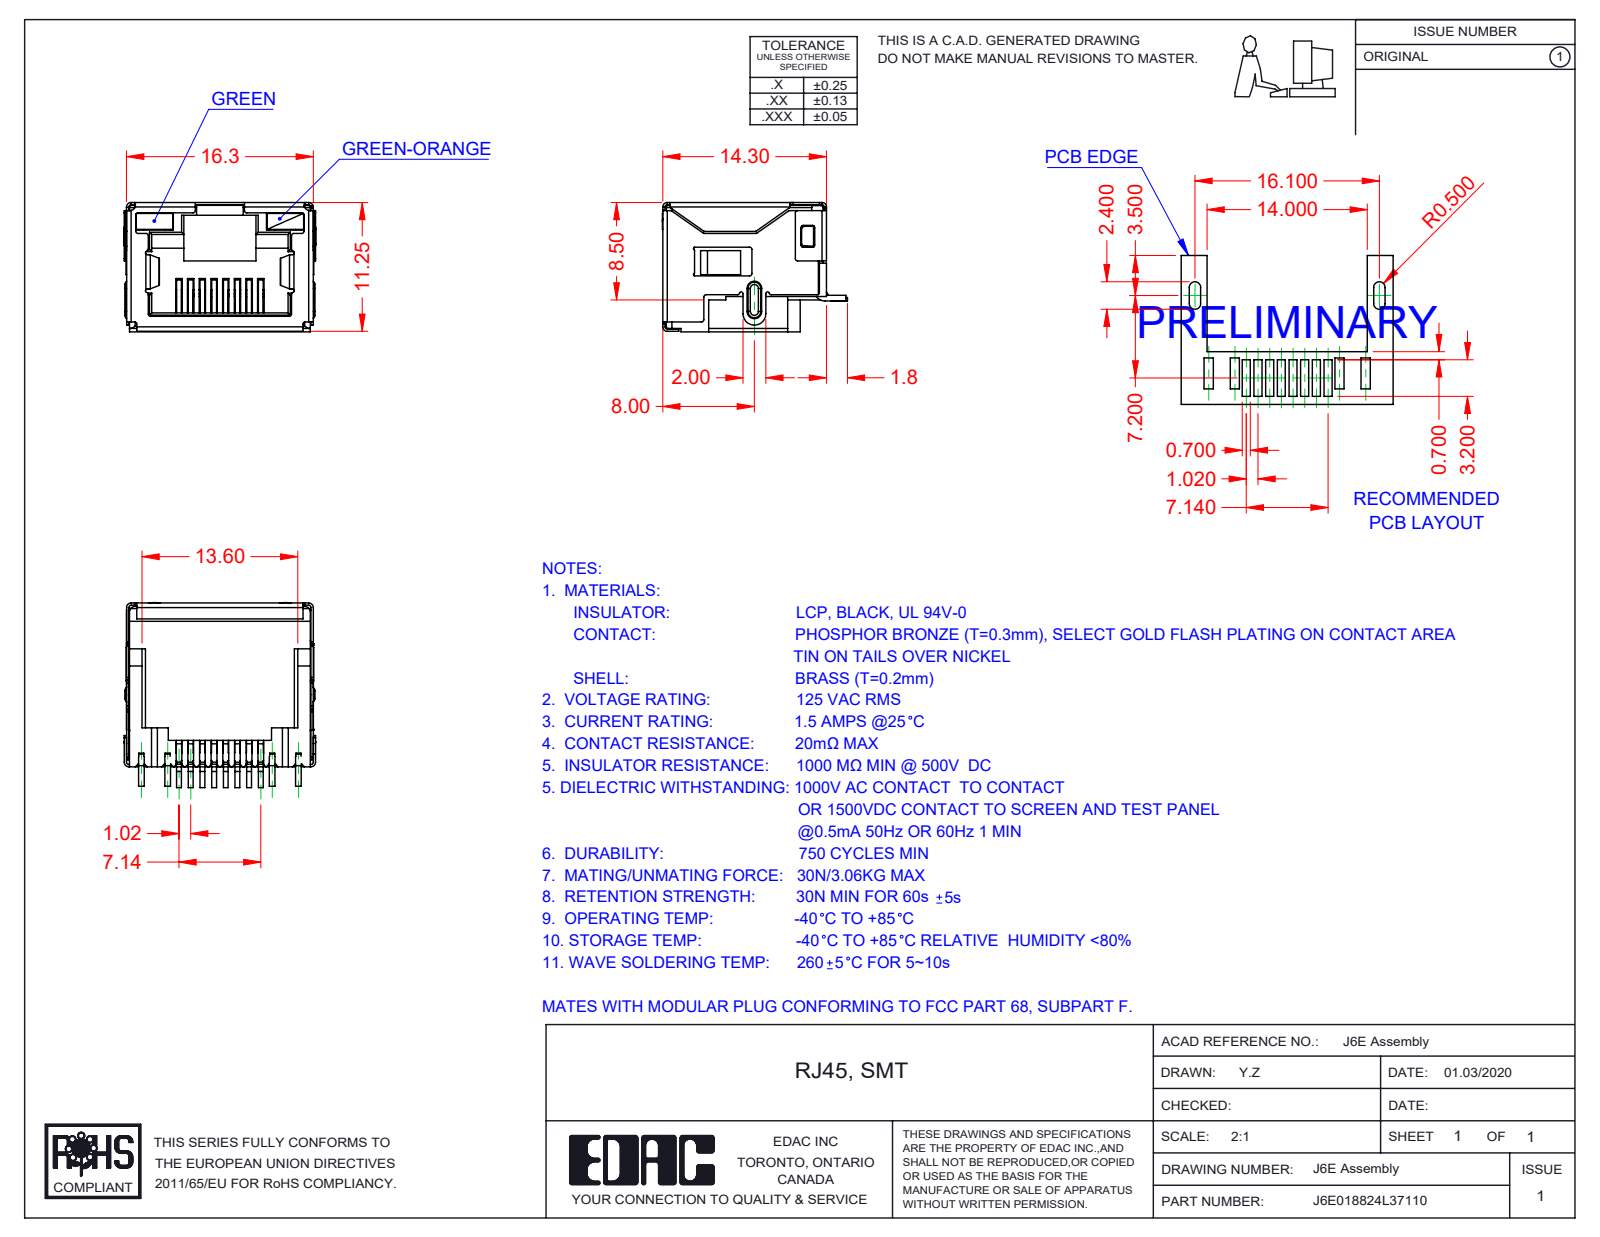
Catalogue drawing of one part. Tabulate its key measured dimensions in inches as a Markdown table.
| quantity | value |
| --- | --- |
| part name | 6E LED LH_3-Green; 6E LED RH_7-Green-Orange; 6E Contacts; 6E Insulator_LED (+2 more) |
| STEP written by | SolidWorks 2016 (CONFIG_CONTROL_DESIGN) |
| units | inches |
| bodies | 12 solids, 1498 faces (1099 planar, 349 cylindrical, 50 other) |
| overall size | 0.659 × 0.636 × 0.445 |
| volume | 0.068 in³ |
| surface area | 6.27 in² |
| partial cylindrical surfaces (radius × count) | 0.008 × 82, 0.01 × 17, 0.016 × 13, 0.02 × 13, 0.004 × 10, 0.006 × 7, 0.012 × 4, 0.039 × 3 |
| main face-to-face distances | 0.435, 0.632, 0.634, 0.624, 0.437, 0.445, 0.094, 0.028, 0.388, 0.019 |
